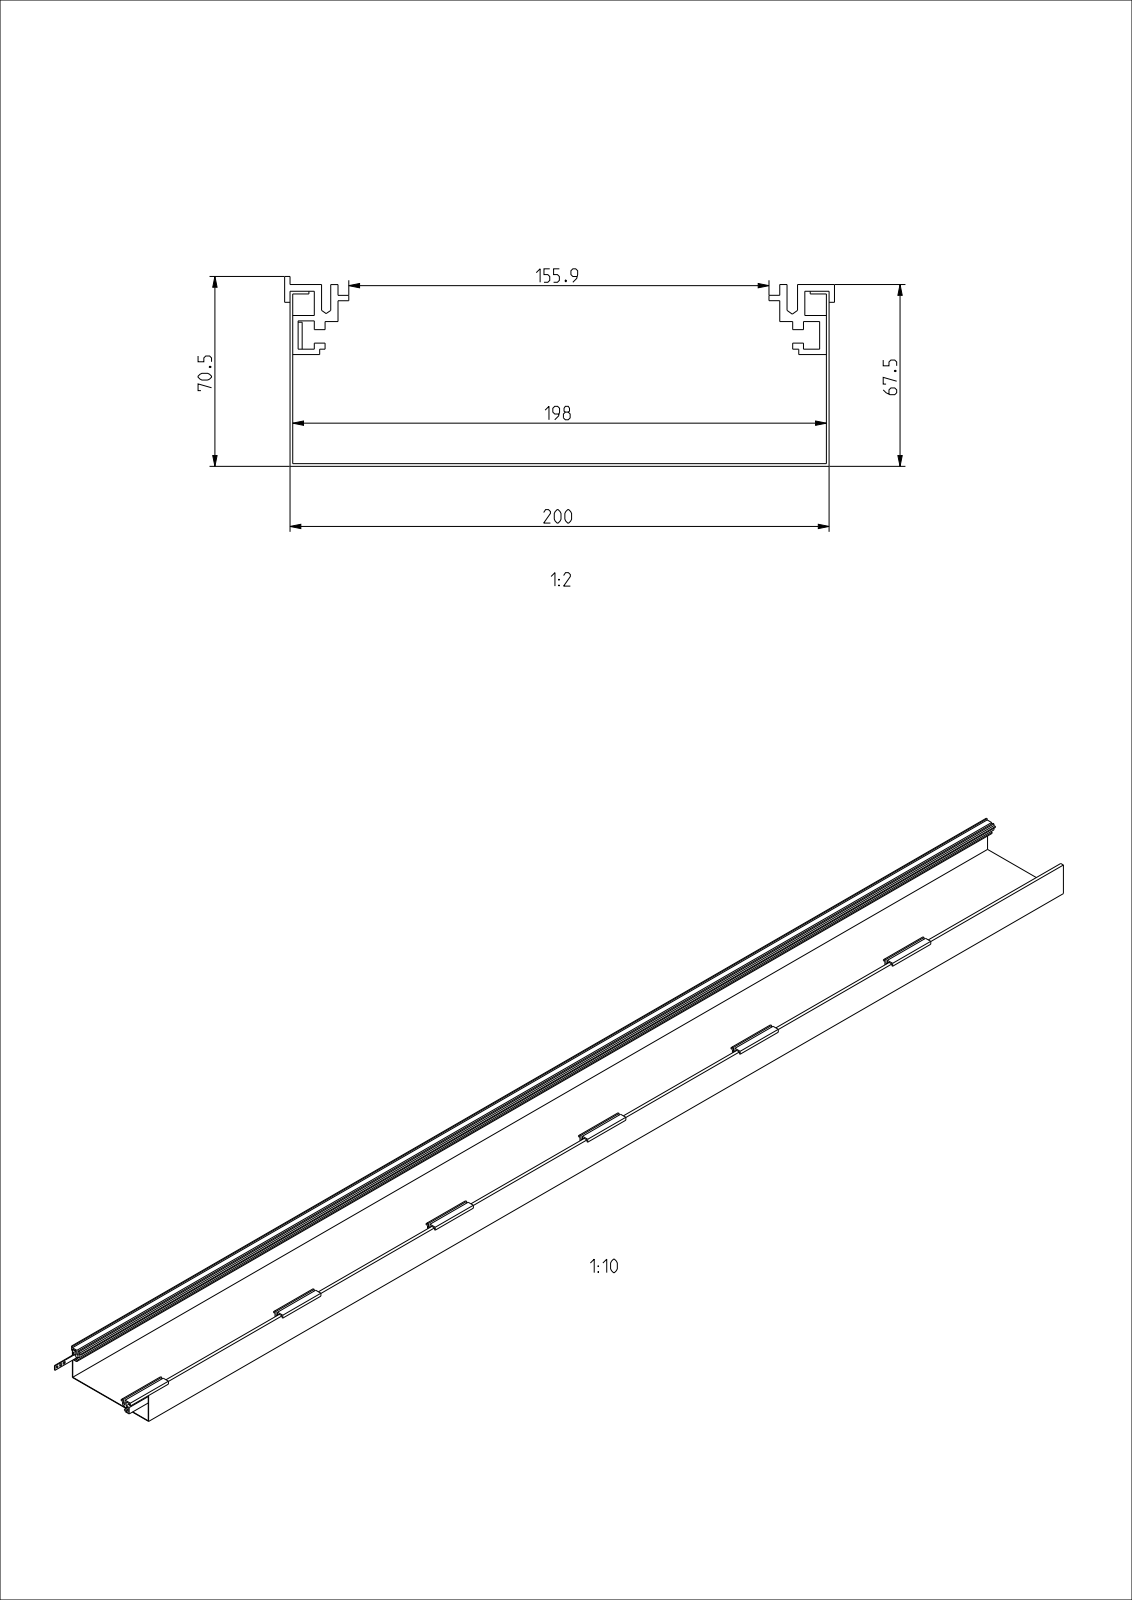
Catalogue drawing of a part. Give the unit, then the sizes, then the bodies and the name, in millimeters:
Units: millimetres
Overall size (bounding box): 2450 × 204 × 70.5
Round holes (diameter × count): ⌀5.5 ×4, ⌀4.2 ×2
Main face-to-face distances: 1, 199, 198, 200, 2, 64, 8, 3, 9, 65
Hole centre spacings: 9.25, 66.5, 18.5, 57.25, 75.75, 48, 85
Volume: 1 461 000 mm³ · Surface area: 2 182 000 mm²
Bodies: 9 solids, 265 faces (253 planar, 12 cylindrical, 0 other)
Part name (STEP PRODUCT): AKU2000701_WANNE_3; AKU_SEITENPROFIL_APA_K24_6_1; ZES_VK180_KUN_3_1; AKU_SEITENPROFIL_APA_O01_4_1 (+1 more)
STEP written by: CREO PARAMETRIC BY PTC INC, 2022281 (AUTOMOTIVE_DESIGN)
